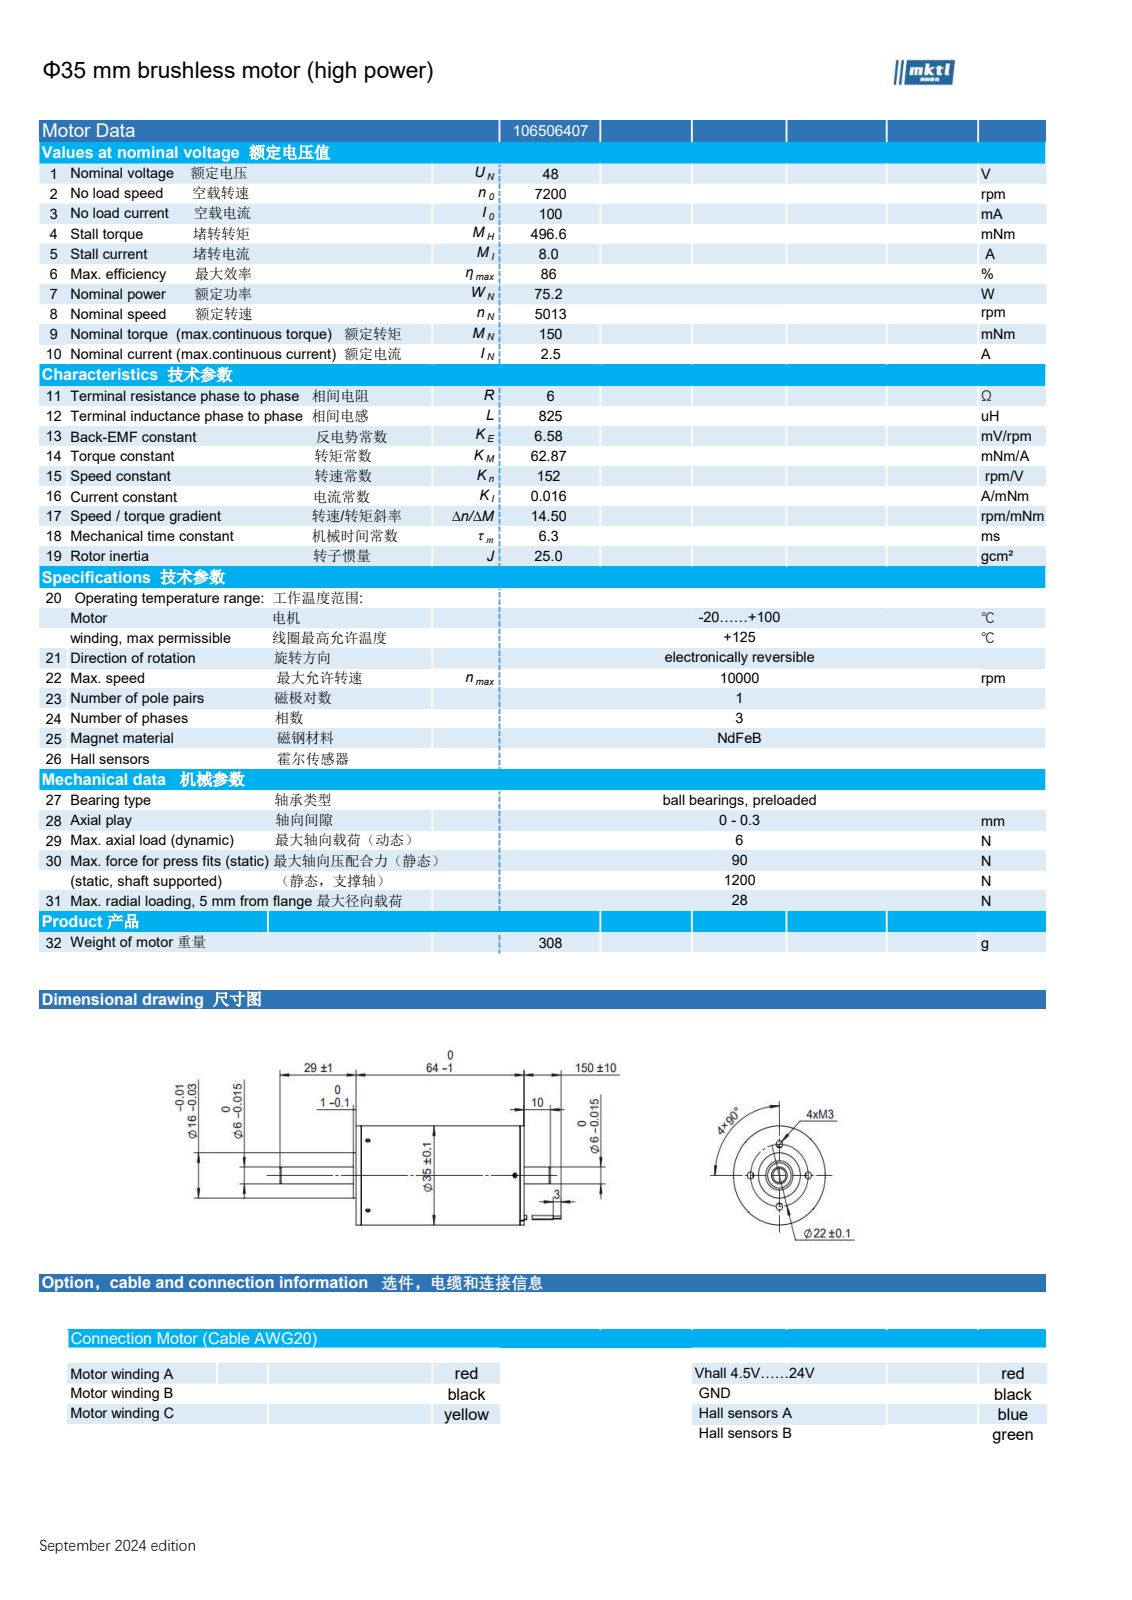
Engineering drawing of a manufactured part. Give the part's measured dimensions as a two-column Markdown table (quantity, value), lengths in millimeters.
| quantity | value |
| --- | --- |
| part name | approval 106506407 |
| STEP written by | SolidWorks 2018 (CONFIG_CONTROL_DESIGN) |
| units | millimeters |
| bodies | 265 solids, 1993 faces (635 planar, 1260 cylindrical, 98 other) |
| overall size | 107.06 × 35 × 35 |
| volume | 57 282 mm³ |
| surface area | 236 511 mm² |
| round holes (diameter × count) | 1.6 × 6, 1 × 4, 2.5 × 4, 1.3 × 3, 1.5 × 3, 1.8 × 3, 2.1 × 3, 5 × 1, 10 × 1, 10.4 × 1, 13 × 1, 14 × 1 |
| round bosses / shafts (diameter × count) | 0.5 × 12, 0.58 × 6, 1.2 × 3, 0.8 × 3, 35 × 1, 33 × 1, 32.9 × 1, 32.8 × 1 |
| partial cylindrical surfaces (radius × count) | 0.75 × 11, 0.3 × 5, 2 × 4, 0.5 × 2, 1 × 2, 8 × 1, 10 × 1, 12.5 × 1 |
| main face-to-face distances | 0.6, 0.4, 0.8, 1, 1.2, 1.4, 1.8, 1.6, 39, 2 |
| hole center spacings | 11, 13.25, 15.56, 14.85, 15, 22, 2.6, 2.61 |
